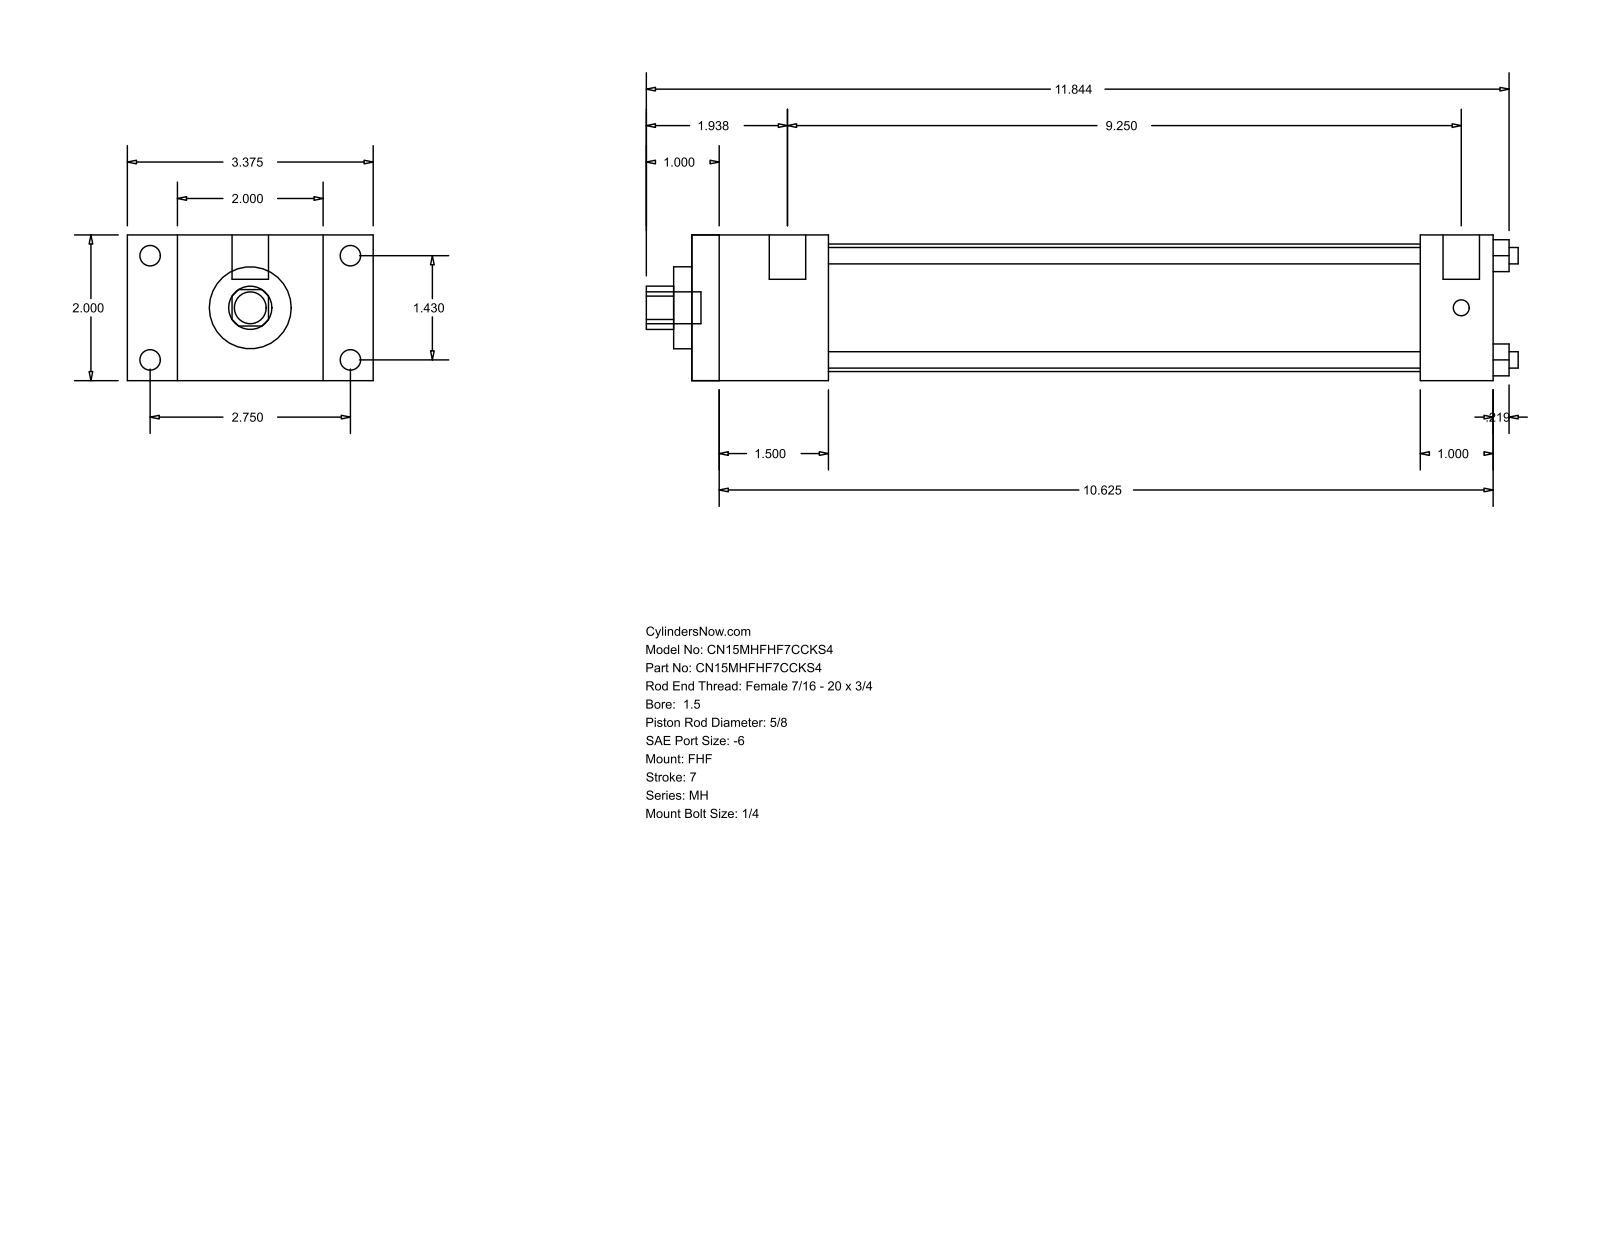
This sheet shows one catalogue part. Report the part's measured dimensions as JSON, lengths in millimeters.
{"part_name": "MH_FHF__0150_0.625", "step_written_by": "GSSL Pune (CONFIG_CONTROL_DESIGN)", "units": "millimeters", "bodies": {"solids": 0, "faces": 88, "planar": 60, "cylindrical": 28, "other": 0}, "overall_size": [304.01, 85.72, 50.8], "round_holes": [[5.71, 4], [15.88, 1], [28.57, 1], [44.45, 1]], "round_bosses_or_shafts": [[7.14, 4], [5.56, 4], [12.7, 2], [11.11, 1]], "partial_cylinders_radius": [[7.54, 1]], "face_to_face_distances": [50.8, 17.46, 68.26, 47.62, 85.72, 279.39, 231.77, 254, 206.38, 25.39], "hole_center_spacings": [25.68, 36.32, 51.36]}
